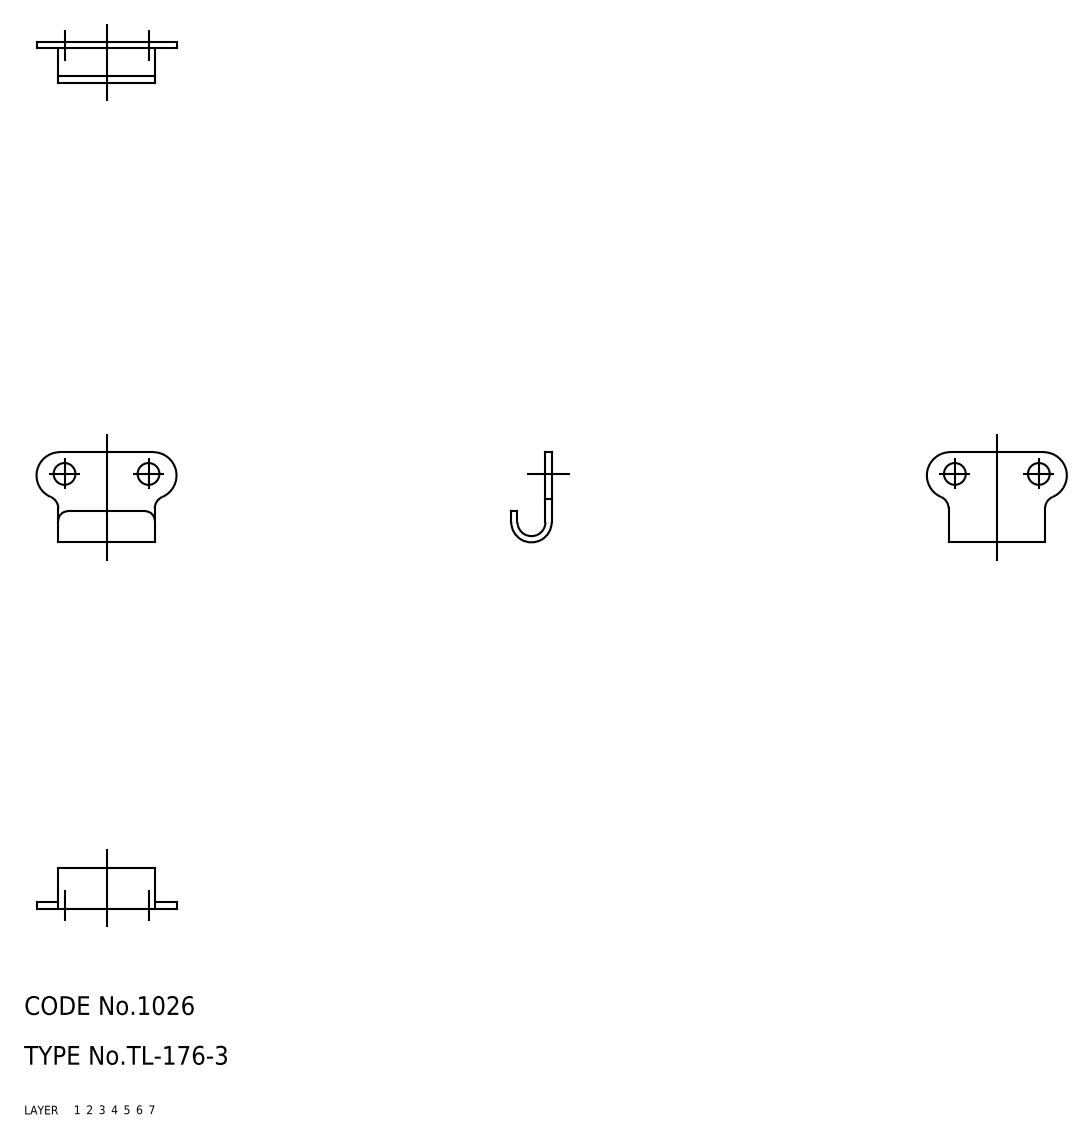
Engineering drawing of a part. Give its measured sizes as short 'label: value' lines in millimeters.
name: keeper
written by: CADfix (AUTOMOTIVE_DESIGN)
unit: mm
bodies: 1 solid, 22 faces (0 planar, 0 cylindrical, 22 other)
size: 22.5 × 14.5 × 6.5
volume: 356 mm³; area: 815 mm²
